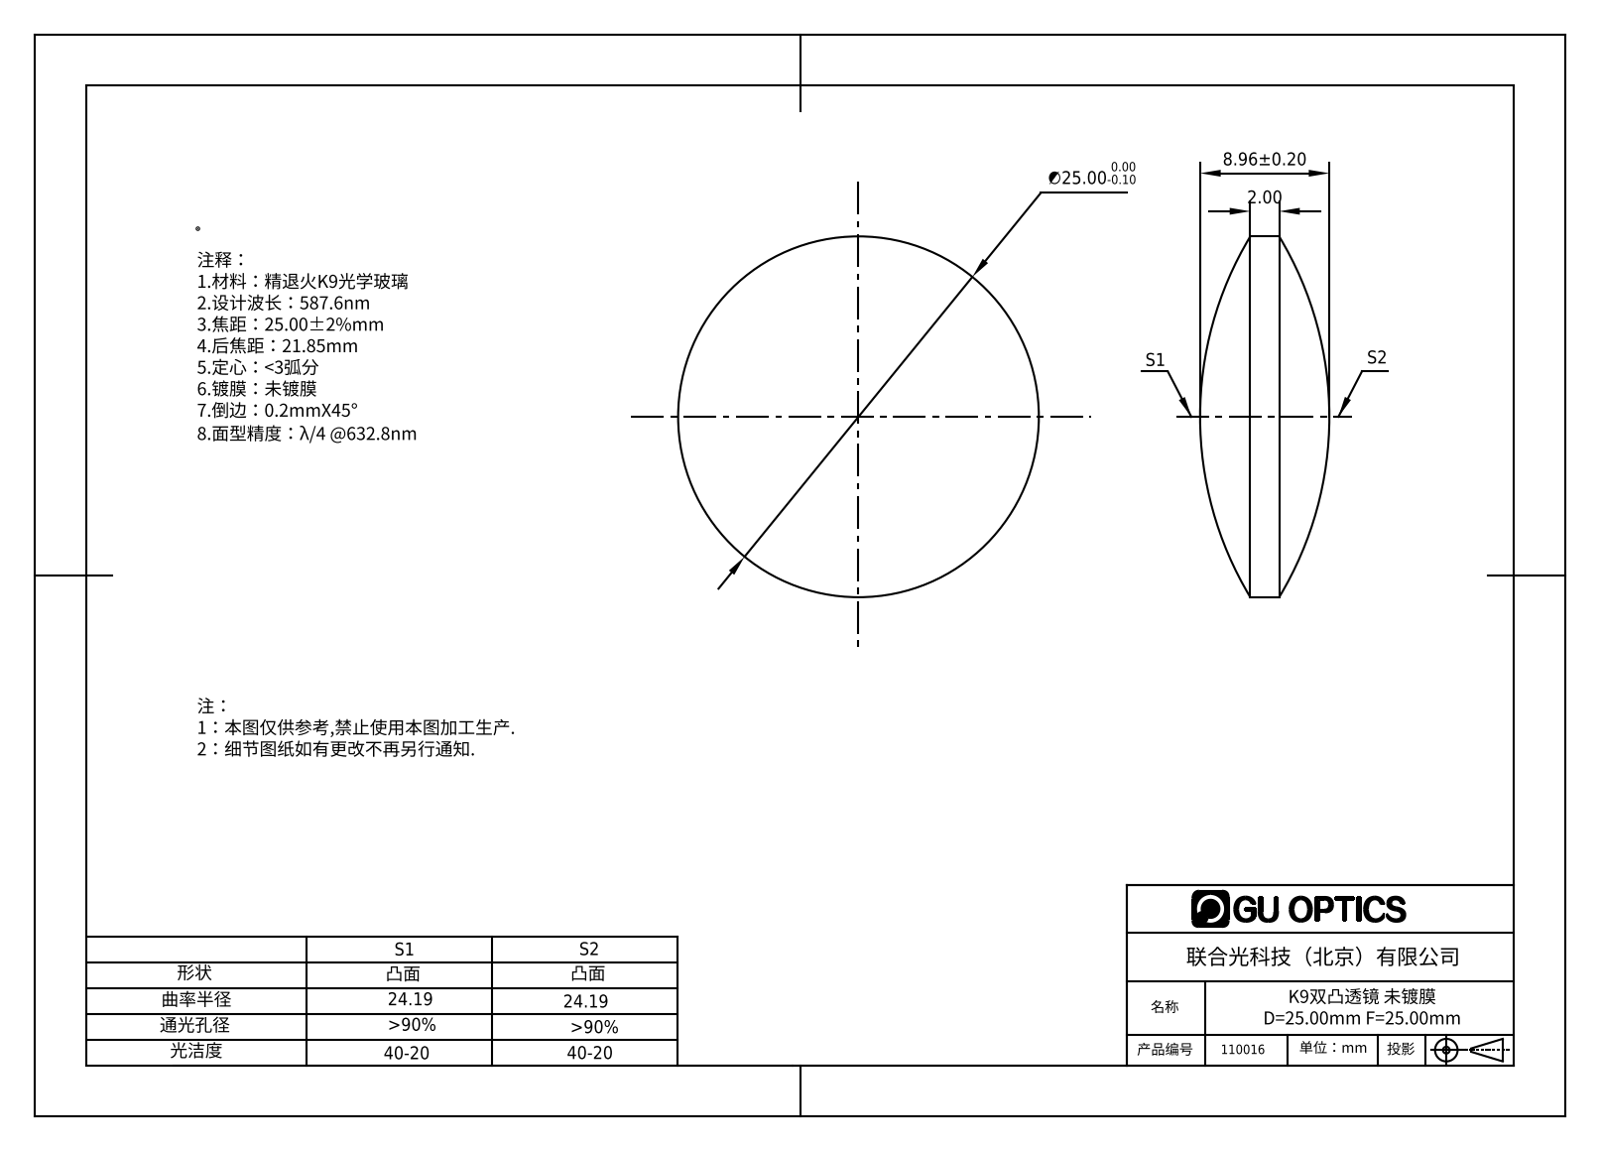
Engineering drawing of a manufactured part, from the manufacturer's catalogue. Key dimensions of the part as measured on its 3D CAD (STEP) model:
Part name (STEP PRODUCT): 110016
STEP written by: SolidWorks 2016 (CONFIG_CONTROL_DESIGN)
Units: millimetres
Bodies: 1 solid, 6 faces (0 planar, 2 cylindrical, 4 other)
Overall size (bounding box): 25 × 25 × 8.96
Volume: 2 734 mm³ · Surface area: 1 215 mm²
Round bosses / shafts (diameter × count): ⌀25 ×1
